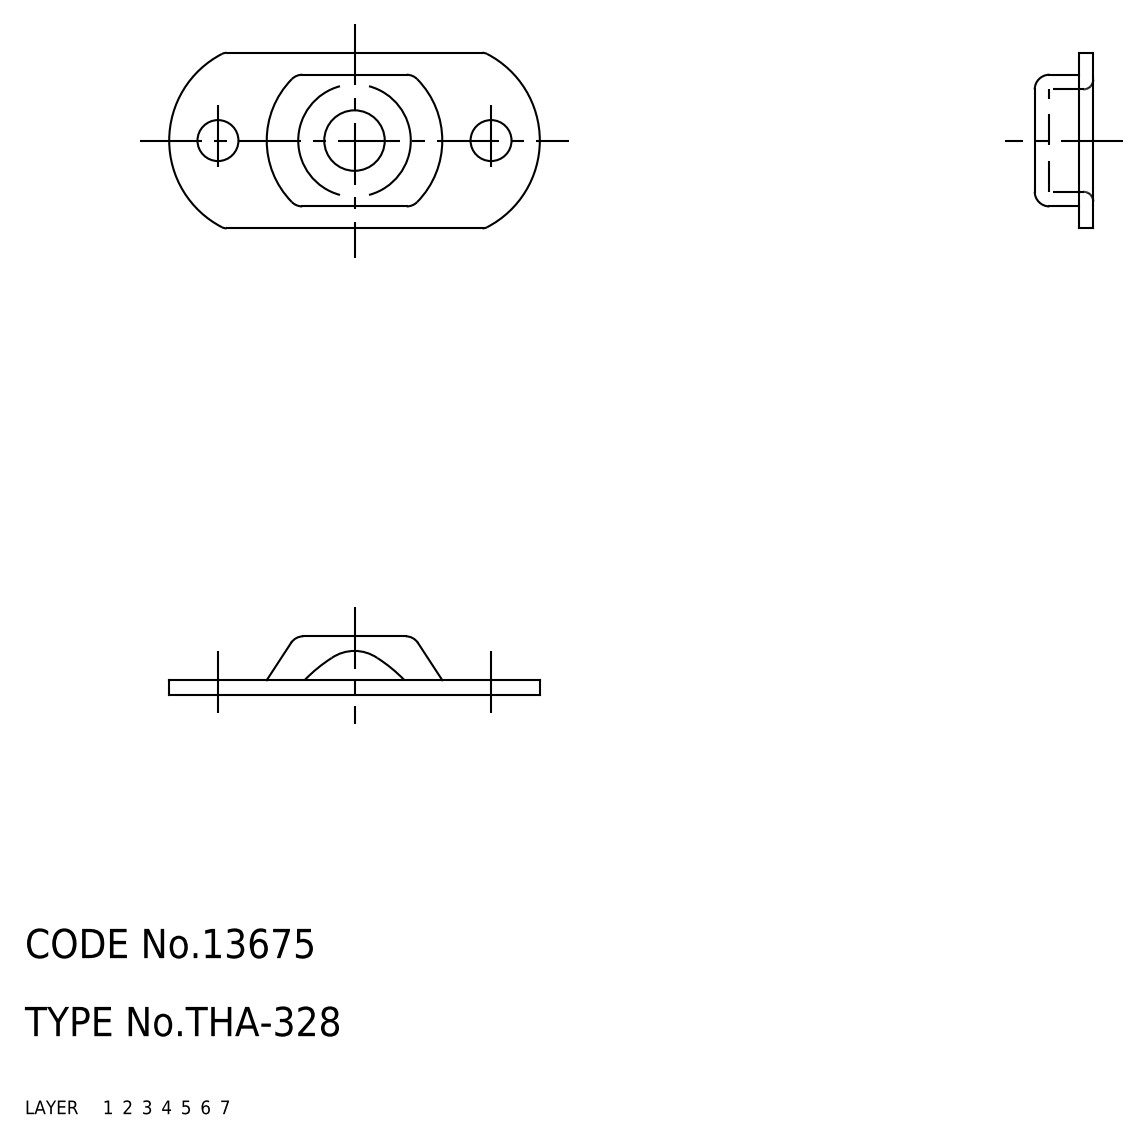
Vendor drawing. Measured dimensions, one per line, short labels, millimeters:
name: THA_328; a
written by: SolidWorks 2015 (AUTOMOTIVE_DESIGN)
unit: mm
bodies: 1 solid, 34 faces (10 planar, 14 cylindrical, 10 other)
size: 38 × 18 × 6
volume: 1 037 mm³; area: 1 599 mm²
holes: 2× ⌀4.2, 1× ⌀6.2
rounds: 4× R1, 2× R1.5, 2× R10
face distances: 1.5, 4.5, 6, 3, 18, 2.25, 15.75, 3.75, 14.25, 12
hole spacings: 14, 28
